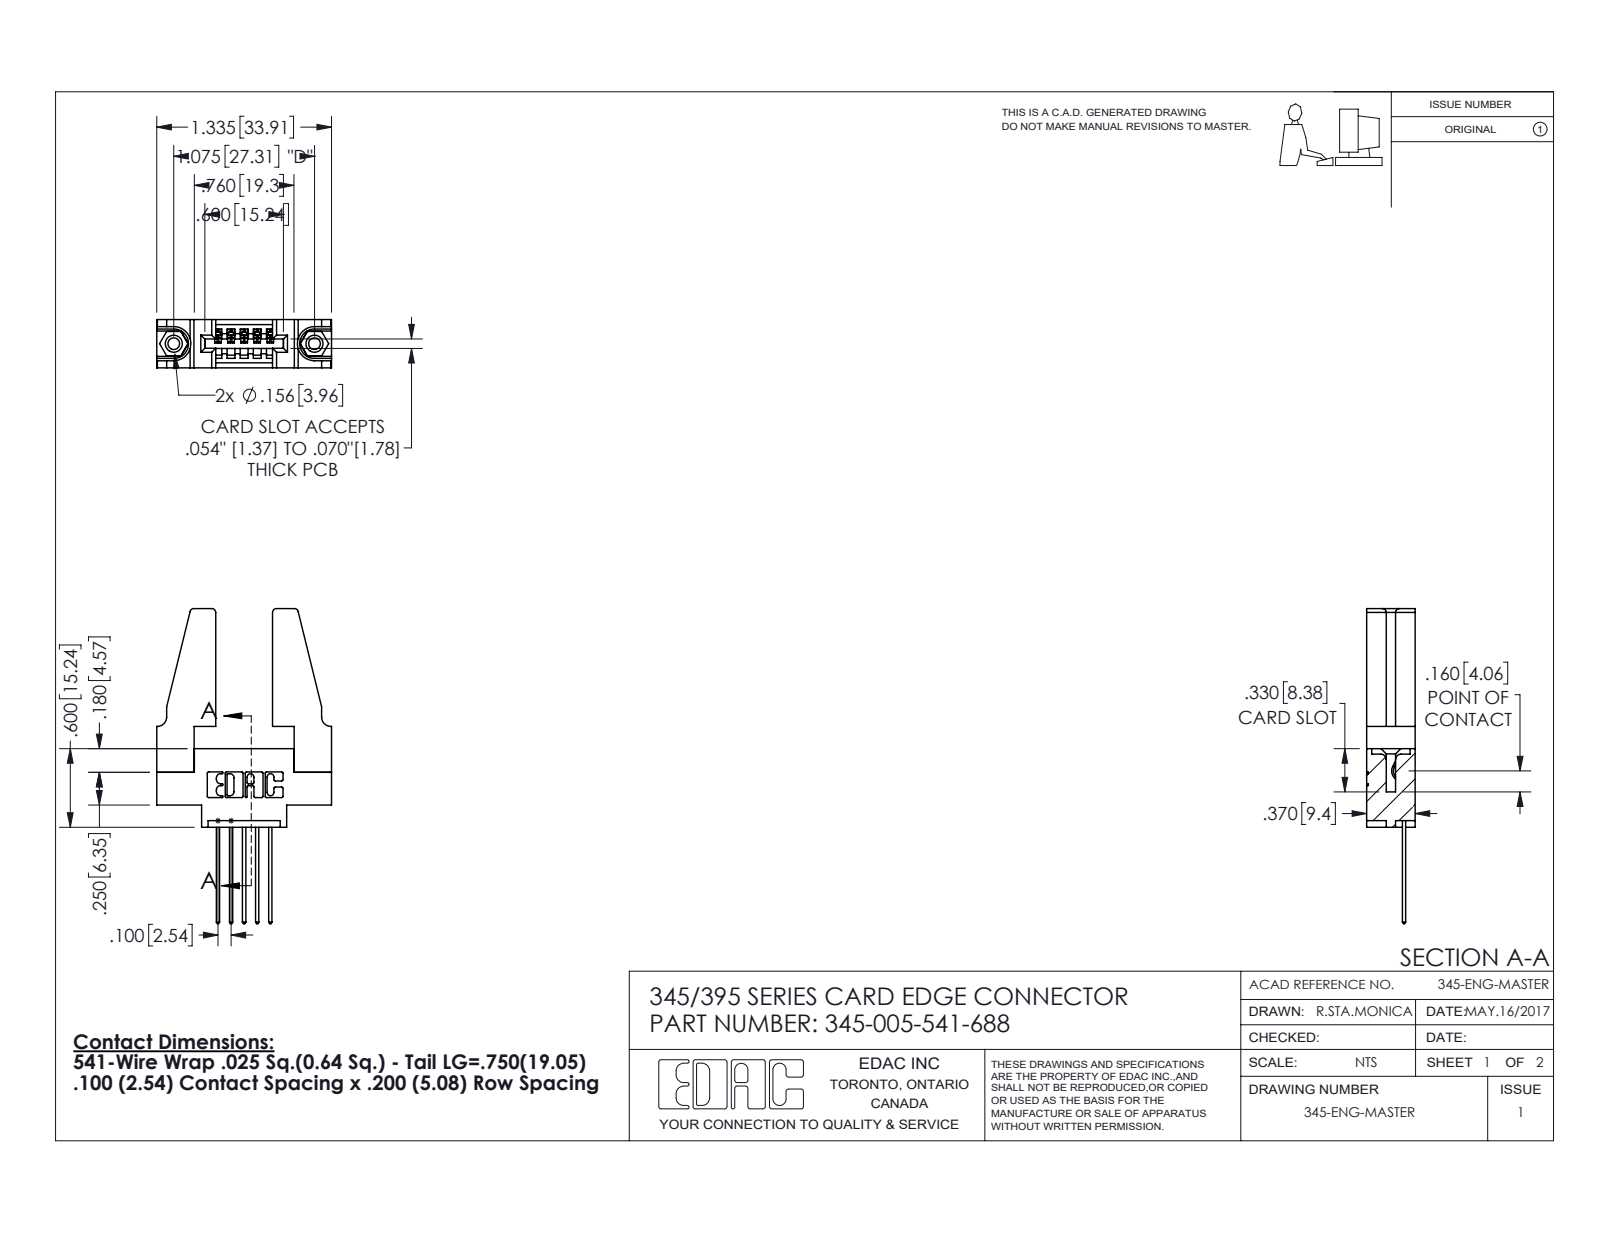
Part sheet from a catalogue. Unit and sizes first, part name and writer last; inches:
Units: inches
Overall size (bounding box): 2.407 × 1.336 × 0.37
Round holes (diameter × count): ⌀0.089 ×2, ⌀0.125 ×2, ⌀0.156 ×2, ⌀0.064 ×1
Round bosses / shafts (diameter × count): ⌀0.155 ×2
Partial cylindrical surfaces — rounded edges, fillets, slot ends (radius × count): R0.01 ×22, R0.006 ×10, R0.01 ×10, R0.03 ×8, R0.007 ×6, R0.031 ×6, R0.026 ×3, R0.031 ×2
Main face-to-face distances: 0.37, 0.072, 0.298, 0.2, 0.148, 0.15, 0.098, 0.272, 0.025, 0.22
Hole centre spacings: 0.27, 0.847, 1.075
Volume: 0.371 in³ · Surface area: 10.23 in²
Bodies: 10 solids, 544 faces (356 planar, 172 cylindrical, 16 other)
Part name (STEP PRODUCT): 345-292-001_345-293-141; 345-005-541-688; 345 Part_0.170 Offset - 0.156 Dia-TH; 345-220-078_345-220-088 (+1 more)
STEP written by: SolidWorks 2016 (CONFIG_CONTROL_DESIGN)
